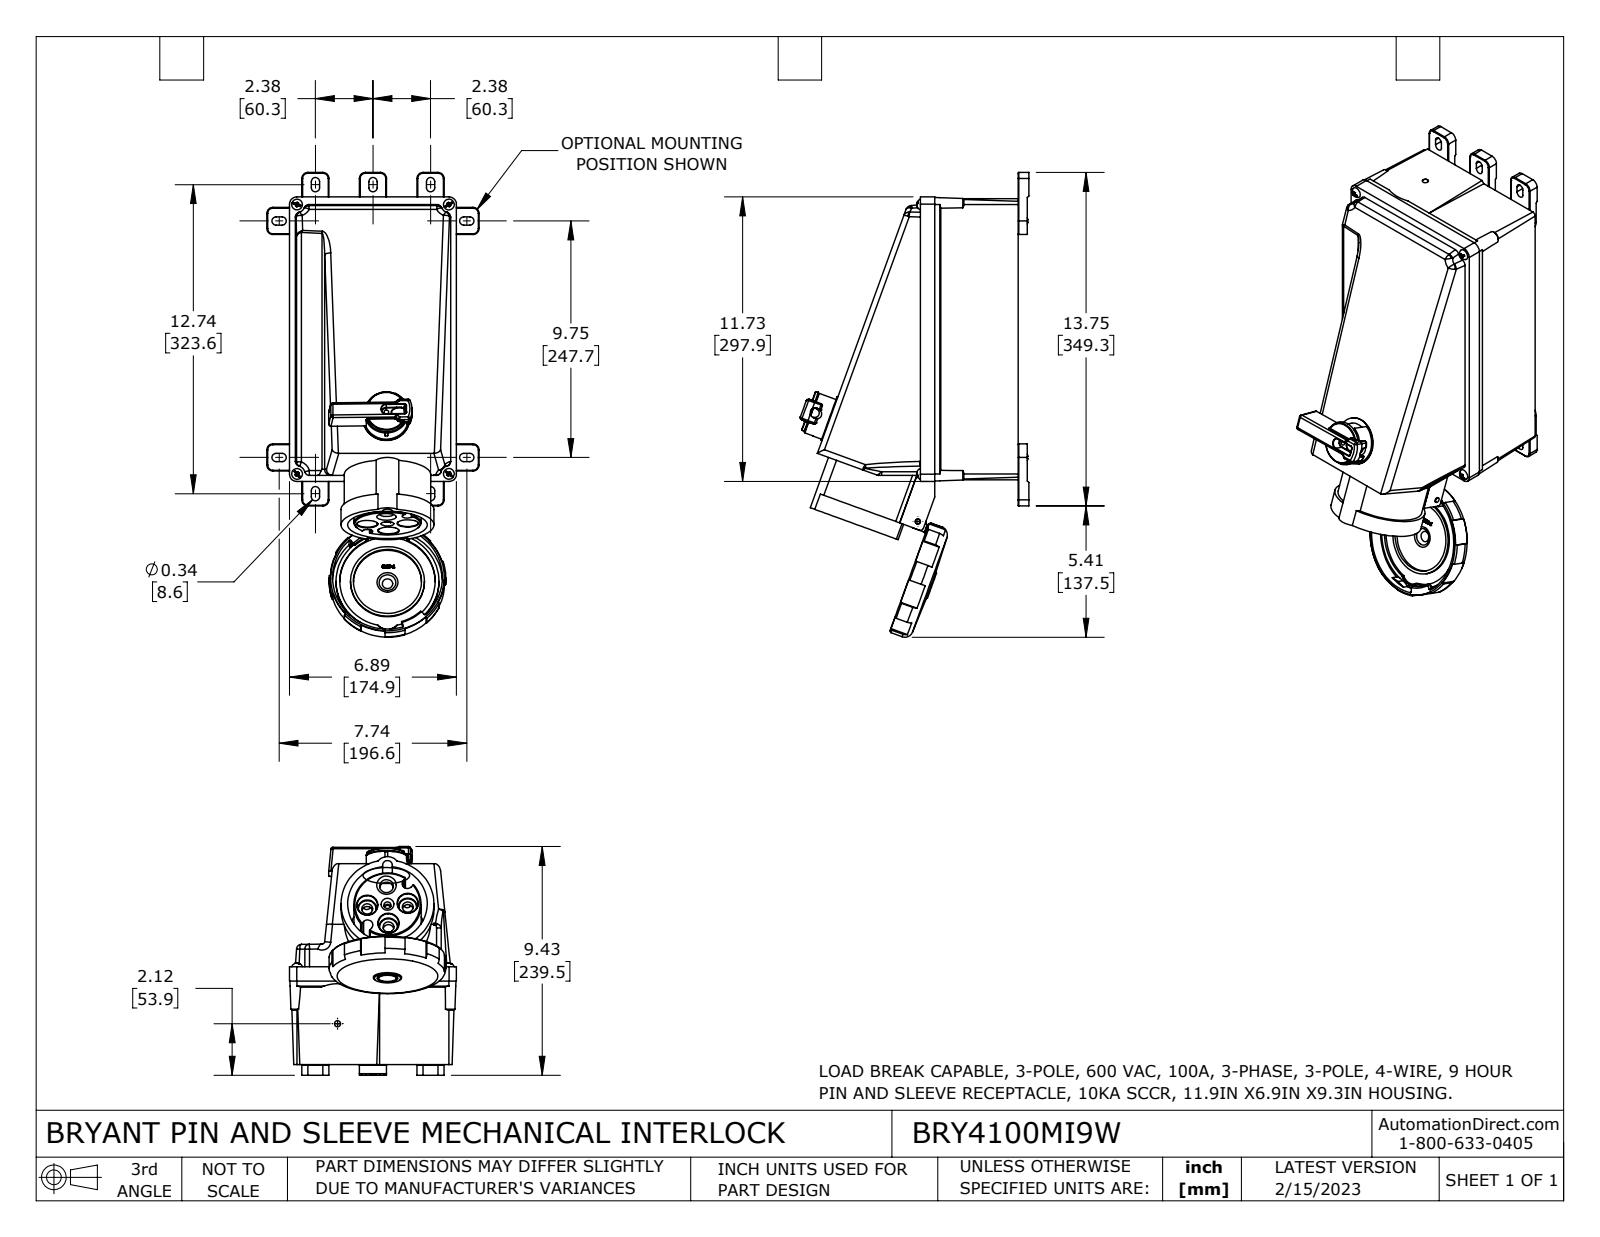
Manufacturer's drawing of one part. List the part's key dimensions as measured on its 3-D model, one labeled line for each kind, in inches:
Part name (STEP PRODUCT): BRY4100MI9W
STEP written by: SolidWorks 2021 (CONFIG_CONTROL_DESIGN)
Units: inches
Bodies: 15 solids, 2241 faces (806 planar, 700 cylindrical, 735 other)
Overall size (bounding box): 19.164 × 9.429 × 6.887
Volume: 478.7 in³ · Surface area: 899.7 in²
Round holes (diameter × count): ⌀0.281 ×5, ⌀0.28 ×3, ⌀0.099 ×2, ⌀0.121 ×2, ⌀0.228 ×2, ⌀0.25 ×2, ⌀0.165 ×1, ⌀0.165 ×1, ⌀0.19 ×1, ⌀0.209 ×1, ⌀0.775 ×1, ⌀0.86 ×1
Round bosses / shafts (diameter × count): ⌀0.263 ×2, ⌀4.244 ×1, ⌀3.048 ×1, ⌀2.834 ×1, ⌀2.775 ×1, ⌀1.92 ×1, ⌀1.244 ×1, ⌀0.8 ×1
Partial cylindrical surfaces — rounded edges, fillets, slot ends (radius × count): R0.015 ×115, R0.03 ×30, R0.08 ×30, R0.09 ×19, R0.25 ×19, R0.02 ×16, R0.075 ×12, R0.17 ×10
Main face-to-face distances: 3.44, 6.073, 0.035, 6.038, 11.594, 4.03, 0.59, 0.12, 0.15, 6.887
Hole centre spacings: 0.69, 0.69, 2.439, 2.44, 5.029, 5.029, 1.195, 1.219
